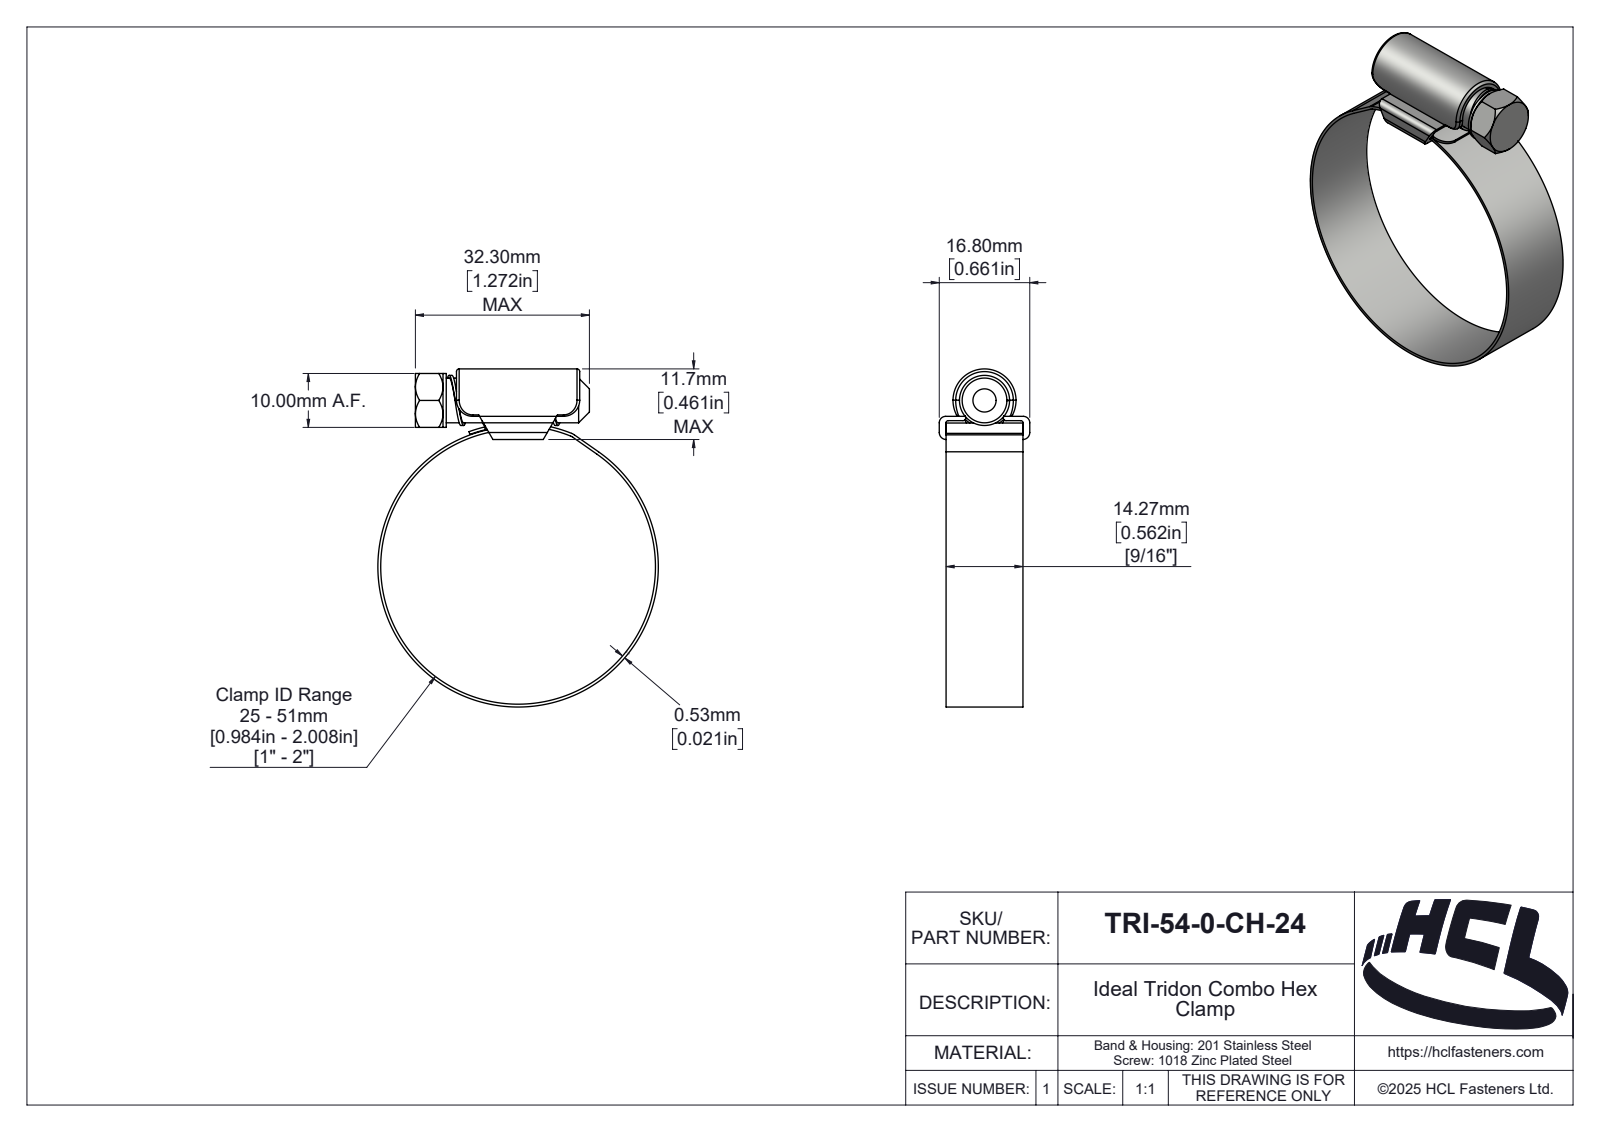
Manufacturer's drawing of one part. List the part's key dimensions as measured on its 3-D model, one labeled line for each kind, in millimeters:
Part name (STEP PRODUCT): TRI-54-0-CH-24
STEP written by: SolidWorks 2025 (AUTOMOTIVE_DESIGN)
Units: millimetres
Bodies: 3 solids, 212 faces (35 planar, 101 cylindrical, 76 other)
Overall size (bounding box): 62.73 × 52.06 × 16.8
Volume: 4 181 mm³ · Surface area: 8 058 mm²
Round holes (diameter × count): ⌀51 ×1
Round bosses / shafts (diameter × count): ⌀52.06 ×1, ⌀10 ×1, ⌀8.3 ×1
Partial cylindrical surfaces — rounded edges, fillets, slot ends (radius × count): R0.5 ×6, R3 ×4, R0.1 ×2, R1.2 ×2, R1.3 ×2, R0.46 ×1, R1.89 ×1, R2 ×1
Main face-to-face distances: 1.2, 14.26, 0.53, 3.5, 2.3, 4.3, 3.1, 0.8, 9.99, 1.27
